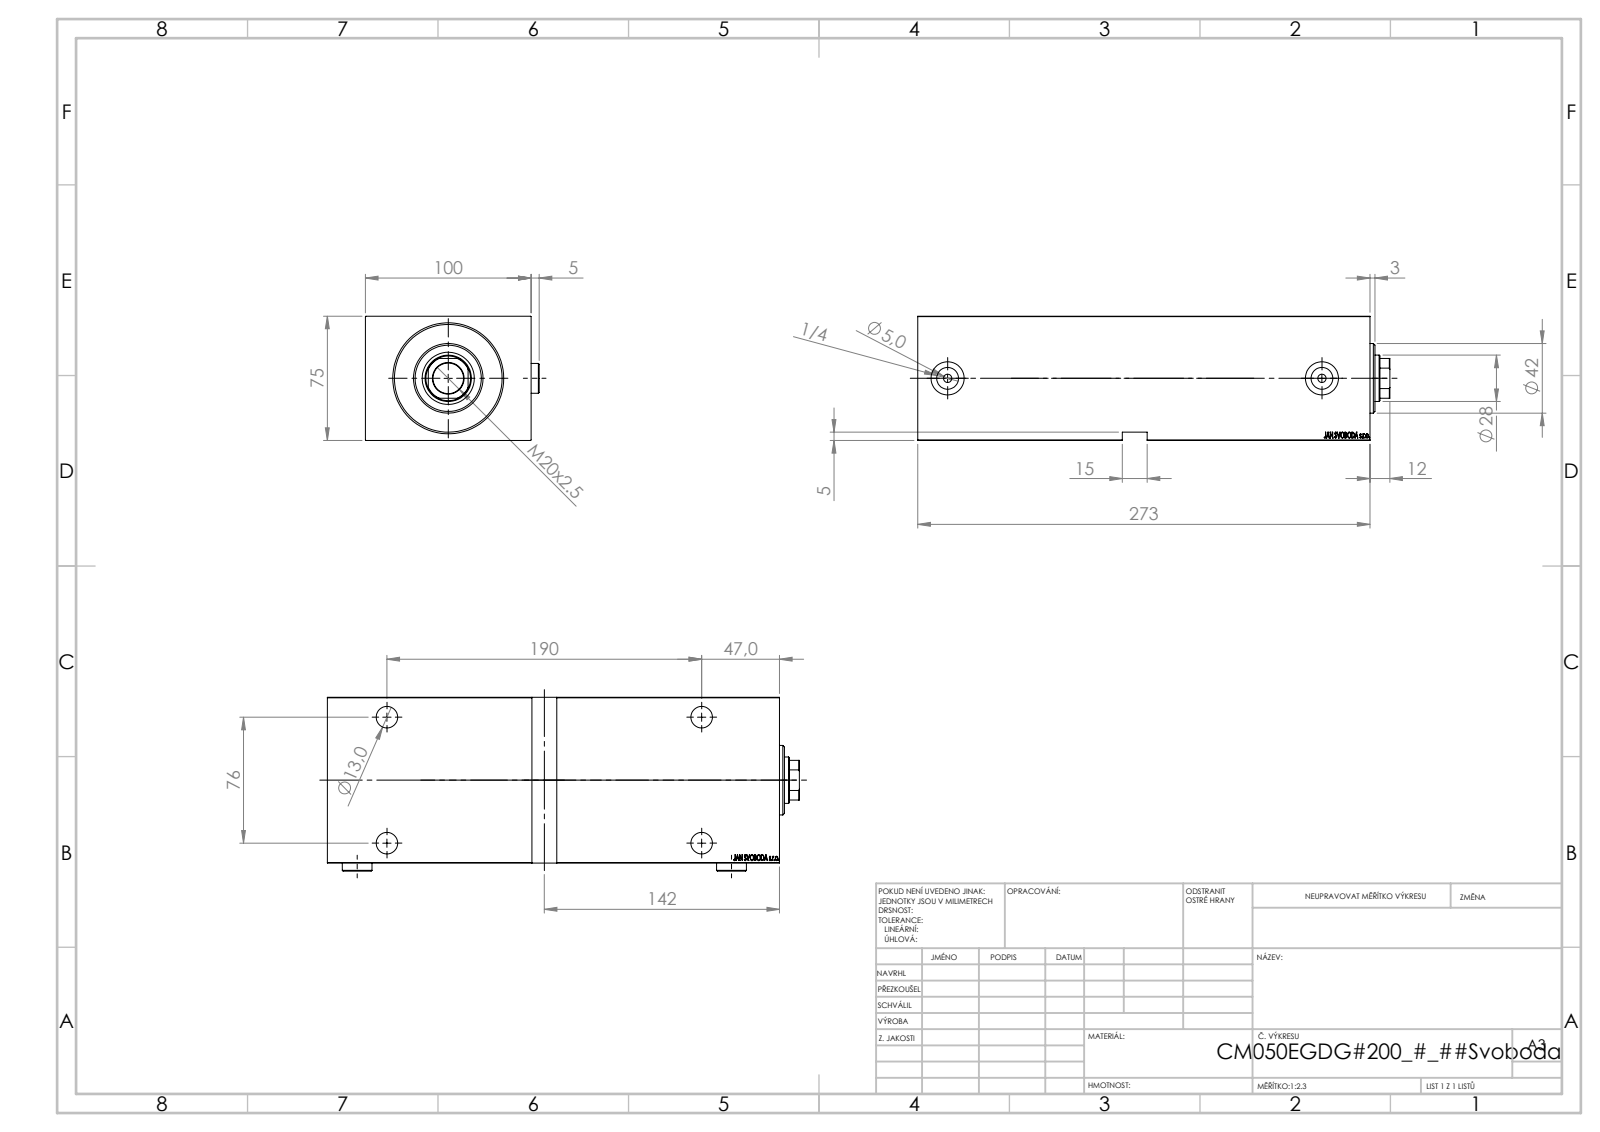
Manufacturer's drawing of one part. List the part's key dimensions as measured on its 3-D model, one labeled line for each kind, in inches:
Part name (STEP PRODUCT): V450CM_E_VCP; V450CM_E_Body; V450CM_VC_B; Zatka_OIL_PORT
STEP written by: SolidWorks 2019 (CONFIG_CONTROL_DESIGN)
Units: inches
Bodies: 5 solids, 912 faces (446 planar, 68 cylindrical, 398 other)
Overall size (bounding box): 11.22 × 4.13 × 2.953
Volume: 105 in³ · Surface area: 328.9 in²
Round holes (diameter × count): ⌀0.512 ×4, ⌀0.748 ×4, ⌀0.197 ×2, ⌀0.518 ×2, ⌀0.787 ×2, ⌀0.728 ×1, ⌀1.102 ×1, ⌀1.24 ×1, ⌀1.969 ×1, ⌀2.559 ×1
Round bosses / shafts (diameter × count): ⌀0.709 ×2, ⌀2.047 ×1, ⌀1.654 ×1
Partial cylindrical surfaces — rounded edges, fillets, slot ends (radius × count): R0.531 ×1
Main face-to-face distances: 2.953, 3.937, 10.748, 0.197, 0.551, 10.197, 10.551, 10, 10.094, 9.543
Hole centre spacings: 2.992, 7.48, 8.057, 8.898
